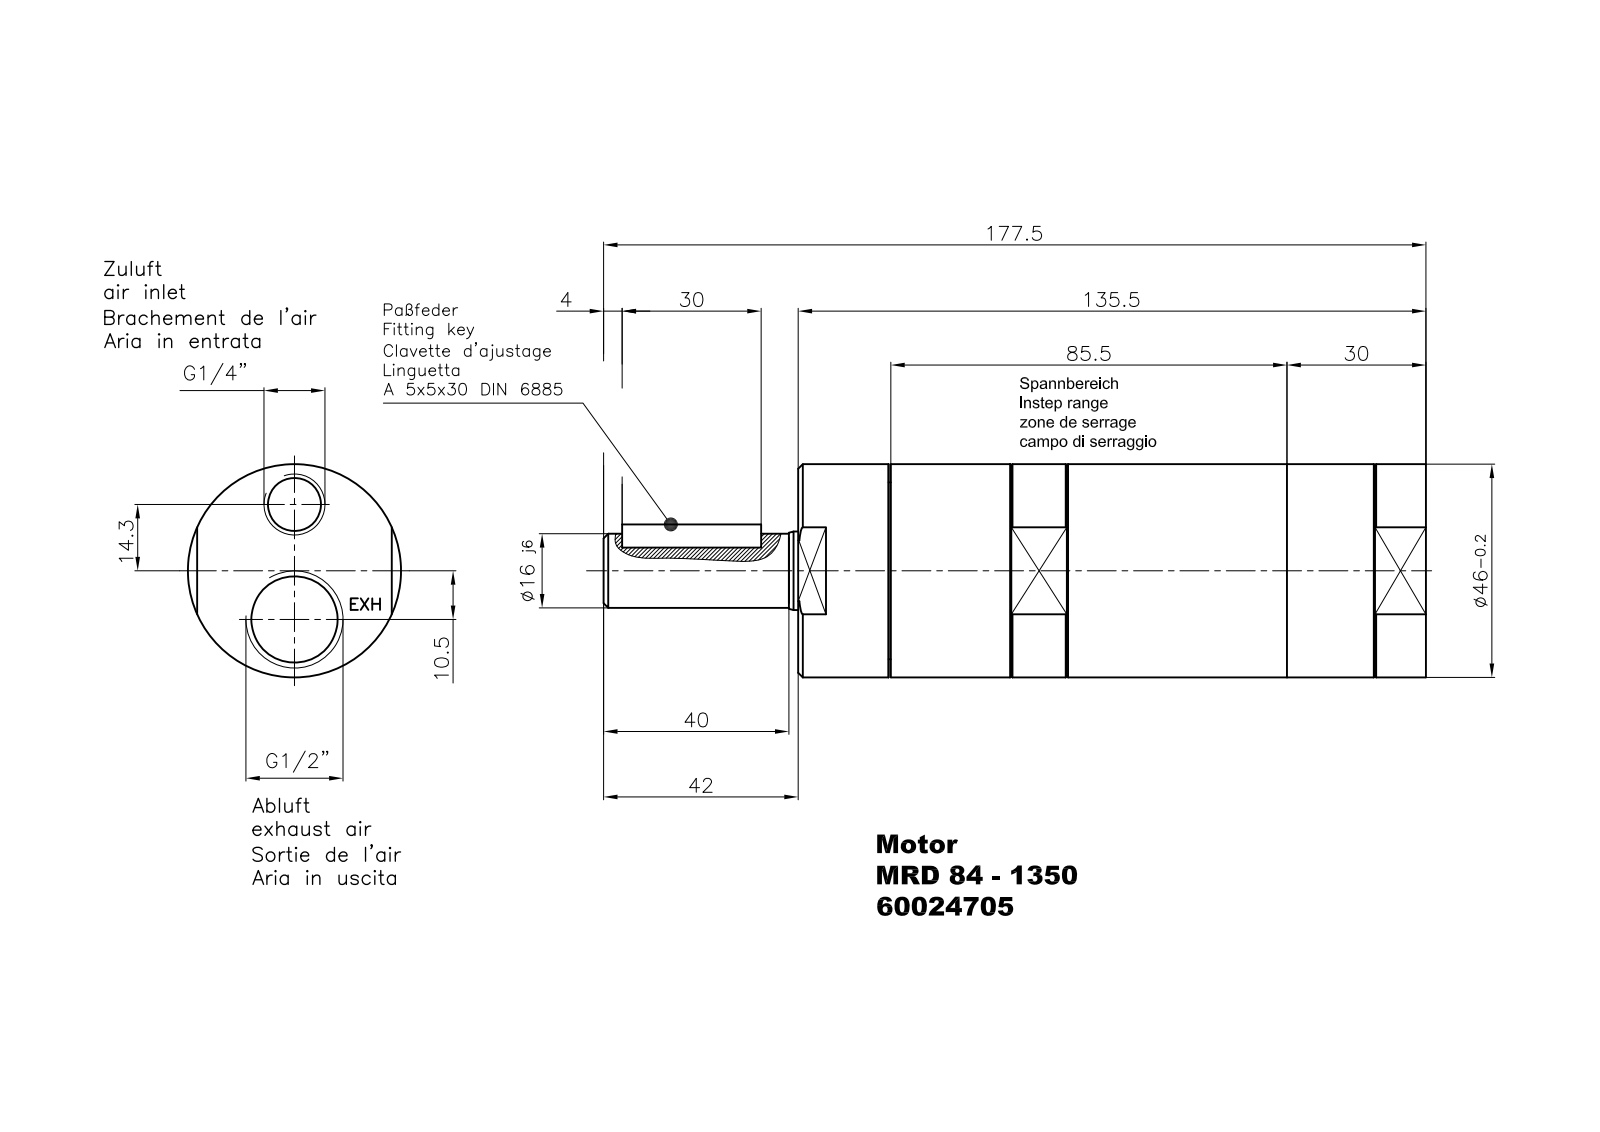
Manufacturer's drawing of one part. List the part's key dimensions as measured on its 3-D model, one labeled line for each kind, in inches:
Part name (STEP PRODUCT): MRD 84-177
STEP written by: Autodesk Inventor 2012 (AUTOMOTIVE_DESIGN)
Units: inches
Bodies: 1 solid, 105 faces (71 planar, 17 cylindrical, 17 other)
Overall size (bounding box): 6.988 × 1.811 × 1.811
Volume: 13.82 in³ · Surface area: 43.7 in²
Round holes (diameter × count): ⌀0.063 ×1, ⌀0.451 ×1, ⌀0.689 ×1, ⌀0.733 ×1
Round bosses / shafts (diameter × count): ⌀1.811 ×1, ⌀1.502 ×1, ⌀0.667 ×1, ⌀0.63 ×1
Partial cylindrical surfaces — rounded edges, fillets, slot ends (radius × count): R0.098 ×2
Main face-to-face distances: 5.335, 1.654, 1.181, 4.154, 0.768, 3.386, 4.567, 4.547, 0.787, 0.02
Hole centre spacings: 0.413, 0.563, 0.976
